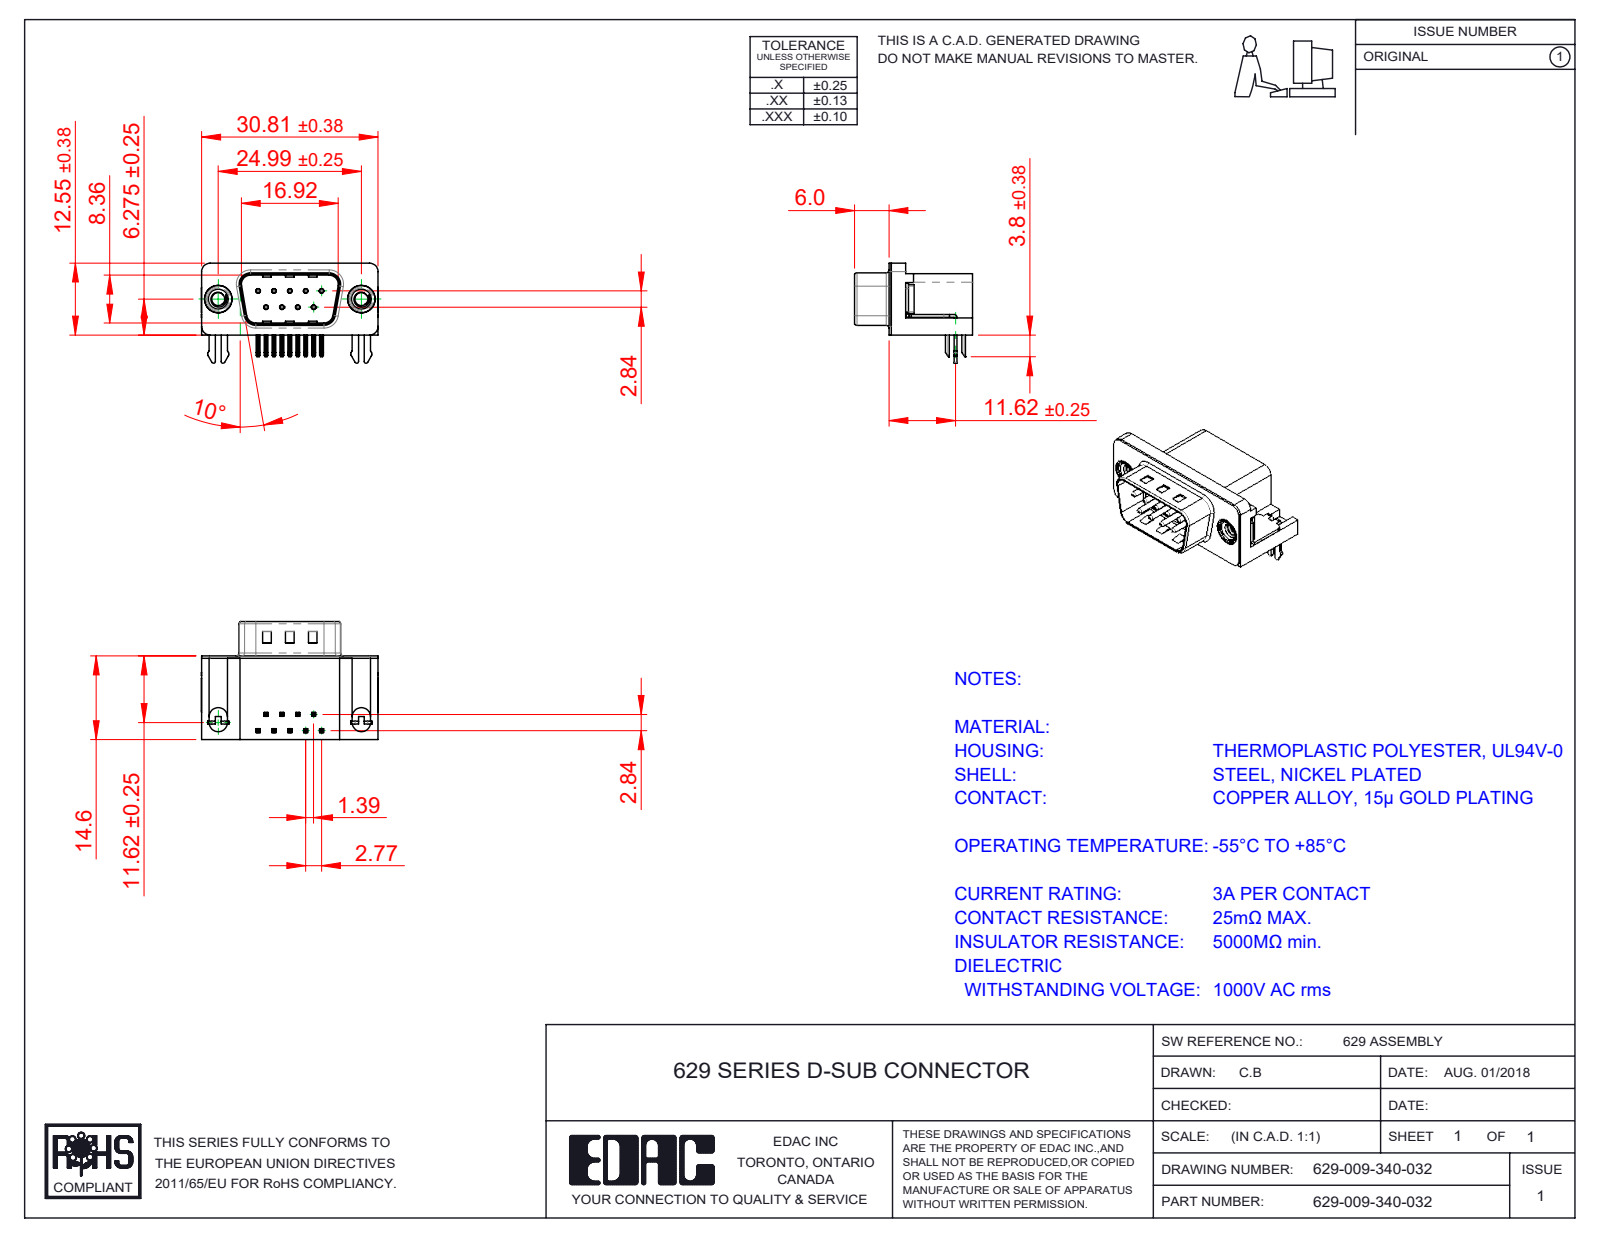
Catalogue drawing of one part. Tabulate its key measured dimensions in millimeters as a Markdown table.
| quantity | value |
| --- | --- |
| part name | 629 Housing_09 Socket; 629 Contact Top; 629 Contact Bottom; 629 Shell_09 Socket (+3 more) |
| STEP written by | SolidWorks 2020 (CONFIG_CONTROL_DESIGN) |
| units | millimeters |
| bodies | 15 solids, 1029 faces (603 planar, 323 cylindrical, 103 other) |
| overall size | 30.89 × 20.6 × 17.48 |
| volume | 3 723 mm³ |
| surface area | 4 764 mm² |
| round holes (diameter × count) | 0.35 × 9, 0.8 × 9, 2.26 × 2, 4 × 2, 4.8 × 2, 5 × 2 |
| round bosses / shafts (diameter × count) | 0.75 × 9, 4.9 × 2, 4.75 × 2, 3.9 × 2 |
| partial cylindrical surfaces (radius × count) | 0.25 × 44, 0.12 × 18, 1 × 16, 0.5 × 14, 1.5 × 8, 1.6 × 8, 0.32 × 4, 0.9 × 4 |
| main face-to-face distances | 0.4, 14.2, 10.35, 0.5, 14.6, 11.7, 2.5, 2.9, 2.1, 6.7 |
| hole center spacings | 3.16, 2.77, 5.54, 5.03, 5.04, 8.31, 7.48, 7.49 |
